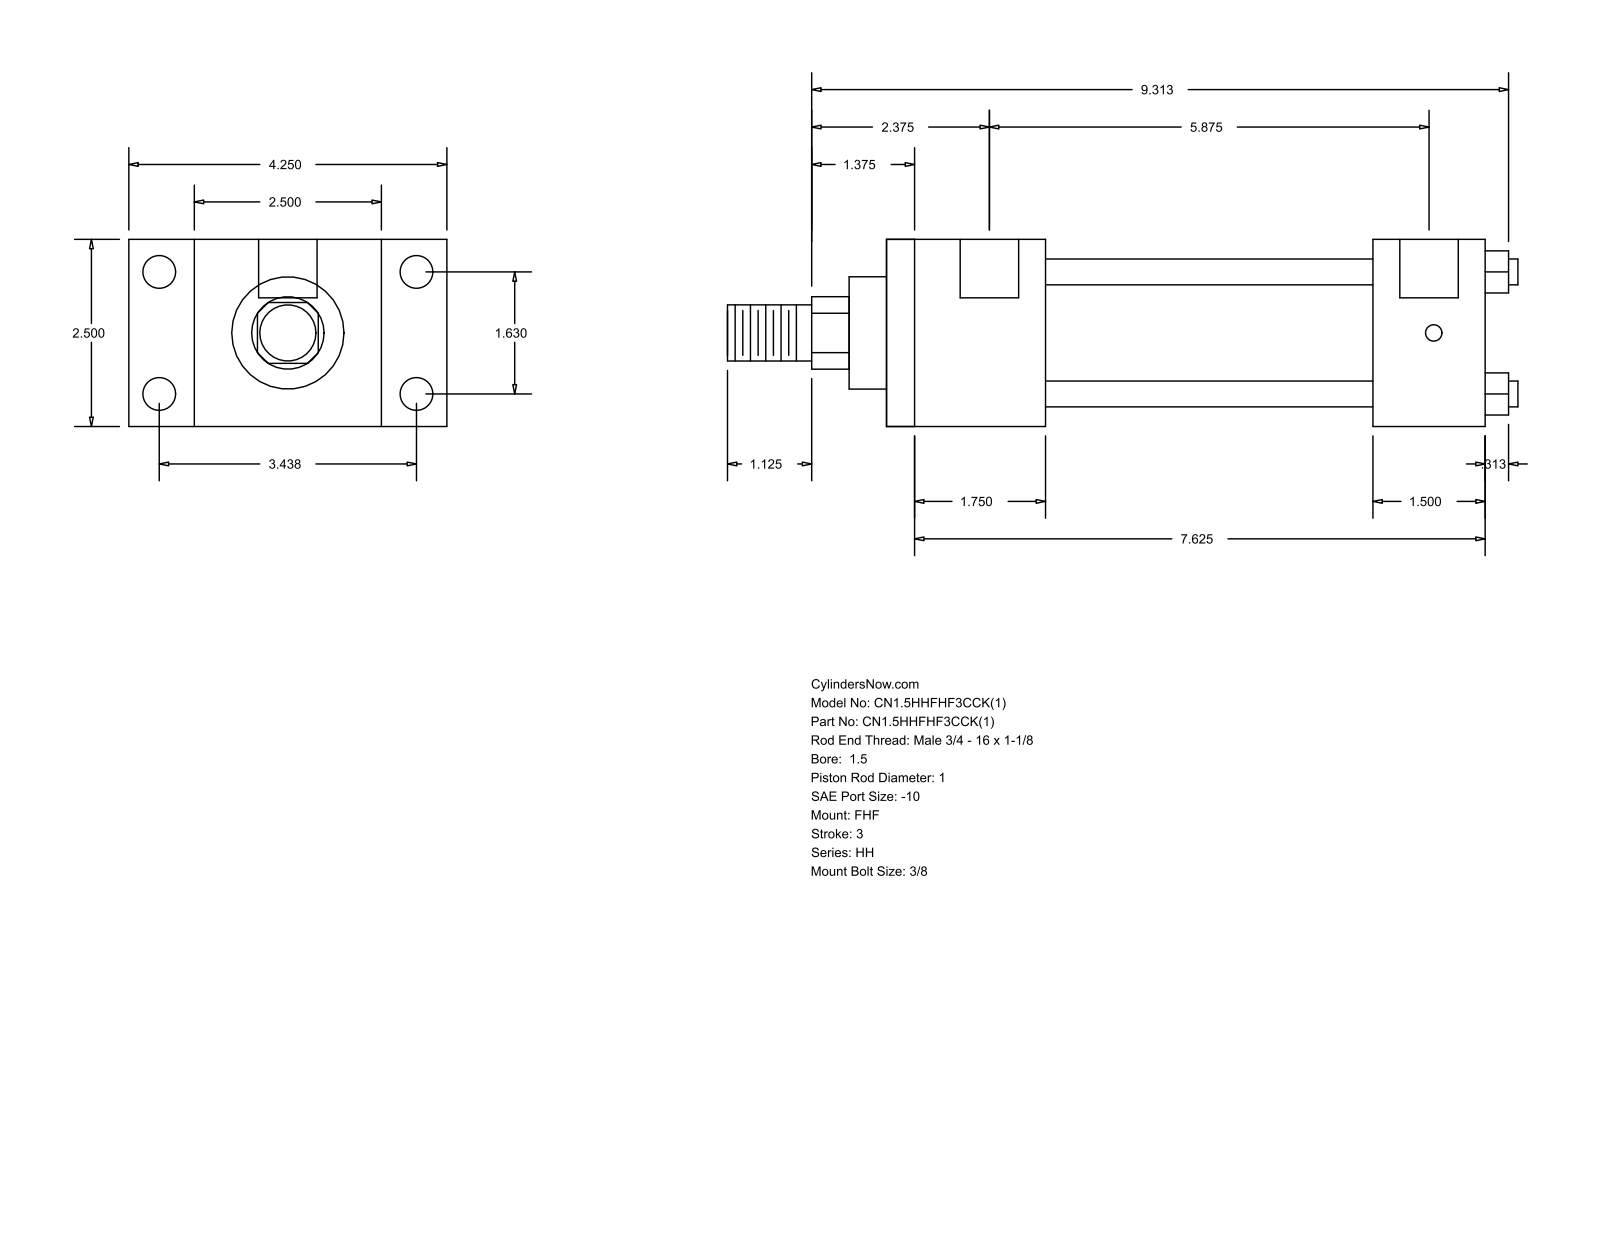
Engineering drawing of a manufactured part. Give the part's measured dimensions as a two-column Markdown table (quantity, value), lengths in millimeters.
| quantity | value |
| --- | --- |
| part name | HH_FHF__0150_1 |
| STEP written by | GSSL Pune (CONFIG_CONTROL_DESIGN) |
| units | millimeters |
| bodies | 0 solids, 88 faces (60 planar, 28 cylindrical, 0 other) |
| overall size | 268.29 × 107.95 × 63.5 |
| round holes (diameter × count) | 5.56 × 4, 11.13 × 4, 19.84 × 2 |
| round bosses / shafts (diameter × count) | 8.76 × 4, 44.45 × 1, 38.1 × 1, 25.4 × 1, 19.05 × 1 |
| partial cylindrical surfaces (radius × count) | 12.29 × 1 |
| main face-to-face distances | 63.5, 22.23, 85.73, 53.98, 107.96, 203.2, 149.22, 38.1, 165.1, 111.12 |
| hole center spacings | 1.59, 41.4, 87.32, 96.64, 150.81, 152.4, 149.22 |
